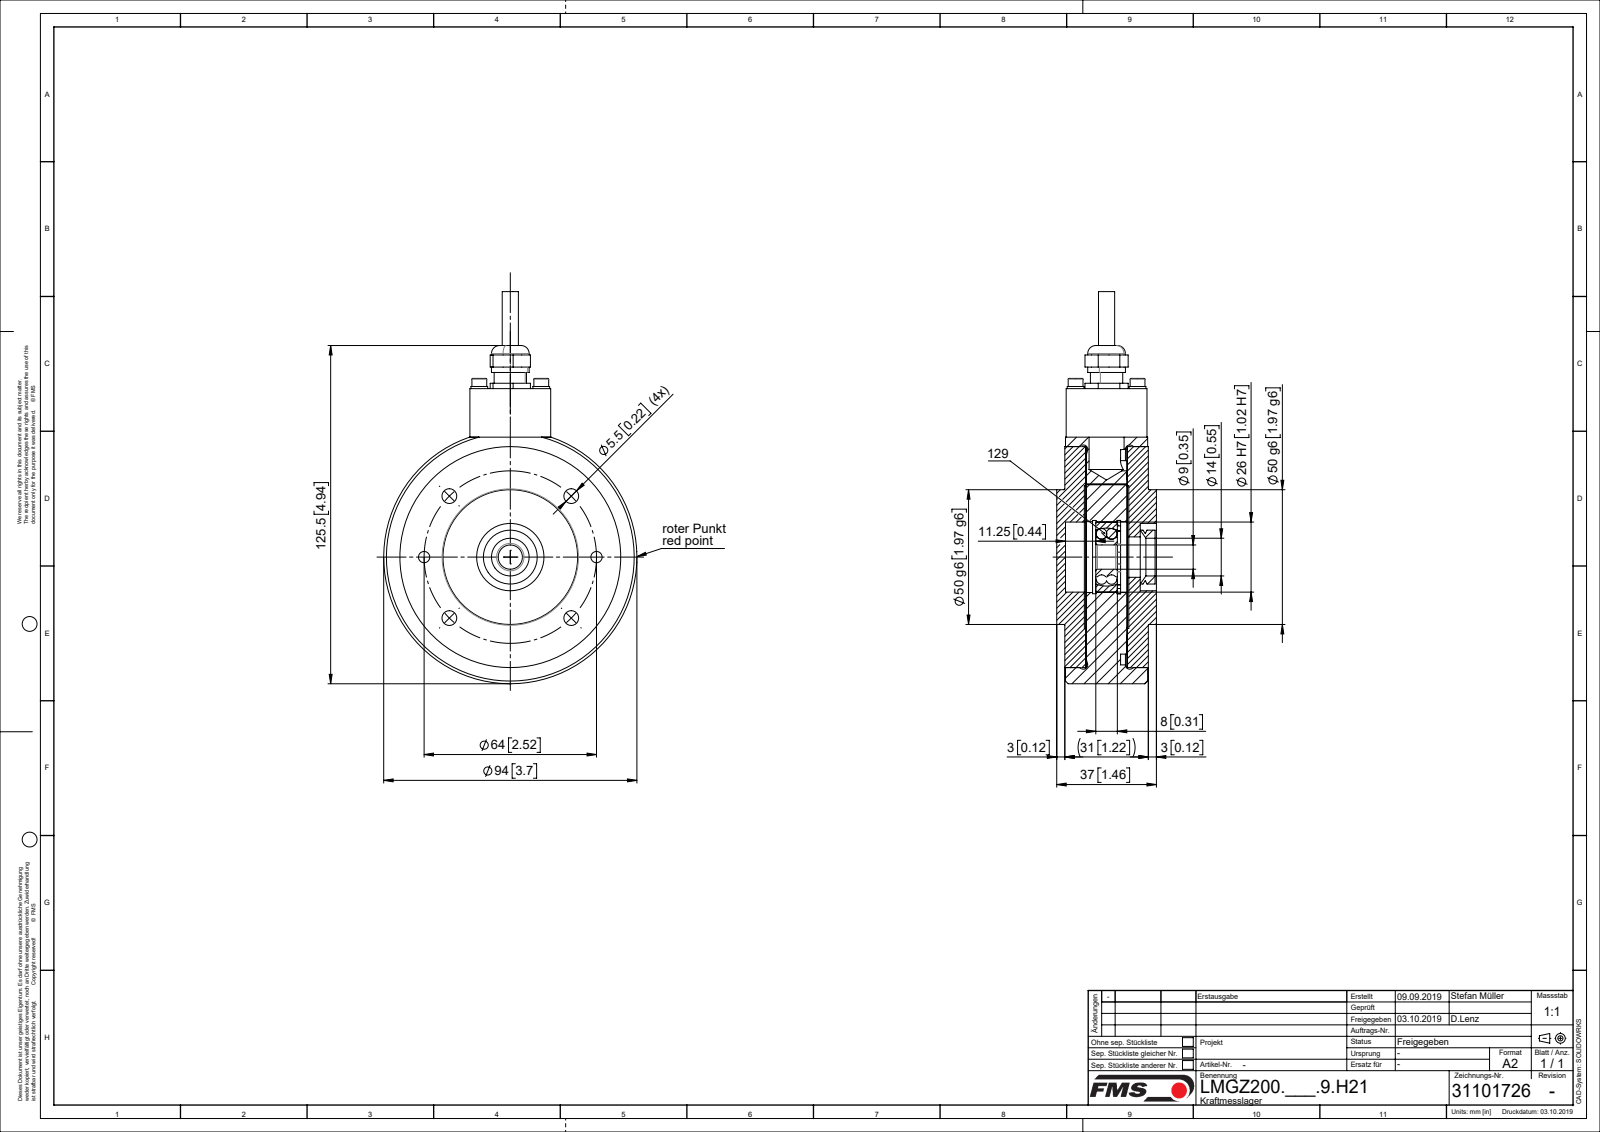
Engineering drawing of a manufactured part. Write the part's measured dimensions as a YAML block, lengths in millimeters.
part_name: "L50040; L4900504; L49012; TEIL1 (+8 more)"
step_written_by: "Mechanical Desktop 2007 (CONFIG_CONTROL_DESIGN)"
units: millimeters
bodies: {solids: 20, faces: 358, planar: 115, cylindrical: 199, other: 44}
overall_size: [131.5, 94, 37]
volume: 219302
surface_area: 81937
round_holes:
  - {diameter: 5.5, count: 6}
  - {diameter: 2.6, count: 4}
  - {diameter: 3.2, count: 4}
  - {diameter: 3.4, count: 4}
  - {diameter: 4.33, count: 4}
  - {diameter: 6.6, count: 4}
  - {diameter: 10, count: 2}
  - {diameter: 6, count: 1}
  - {diameter: 9, count: 1}
  - {diameter: 11.28, count: 1}
  - {diameter: 14, count: 1}
  - {diameter: 15, count: 1}
round_bosses_or_shafts:
  - {diameter: 6.2, count: 4}
  - {diameter: 5.5, count: 4}
  - {diameter: 3, count: 4}
  - {diameter: 8, count: 2}
  - {diameter: 5, count: 2}
  - {diameter: 94, count: 1}
  - {diameter: 82, count: 1}
  - {diameter: 50, count: 1}
partial_cylinders:
  - {radius: 8, count: 2}
face_to_face_distances: [15.25, 15, 23.25, 7.75, 23, 8, 15.5, 0.5, 7.25, 11]
hole_center_spacings: [32, 16.26, 23, 24.49, 45.26, 59.13, 62.77, 12.48]
